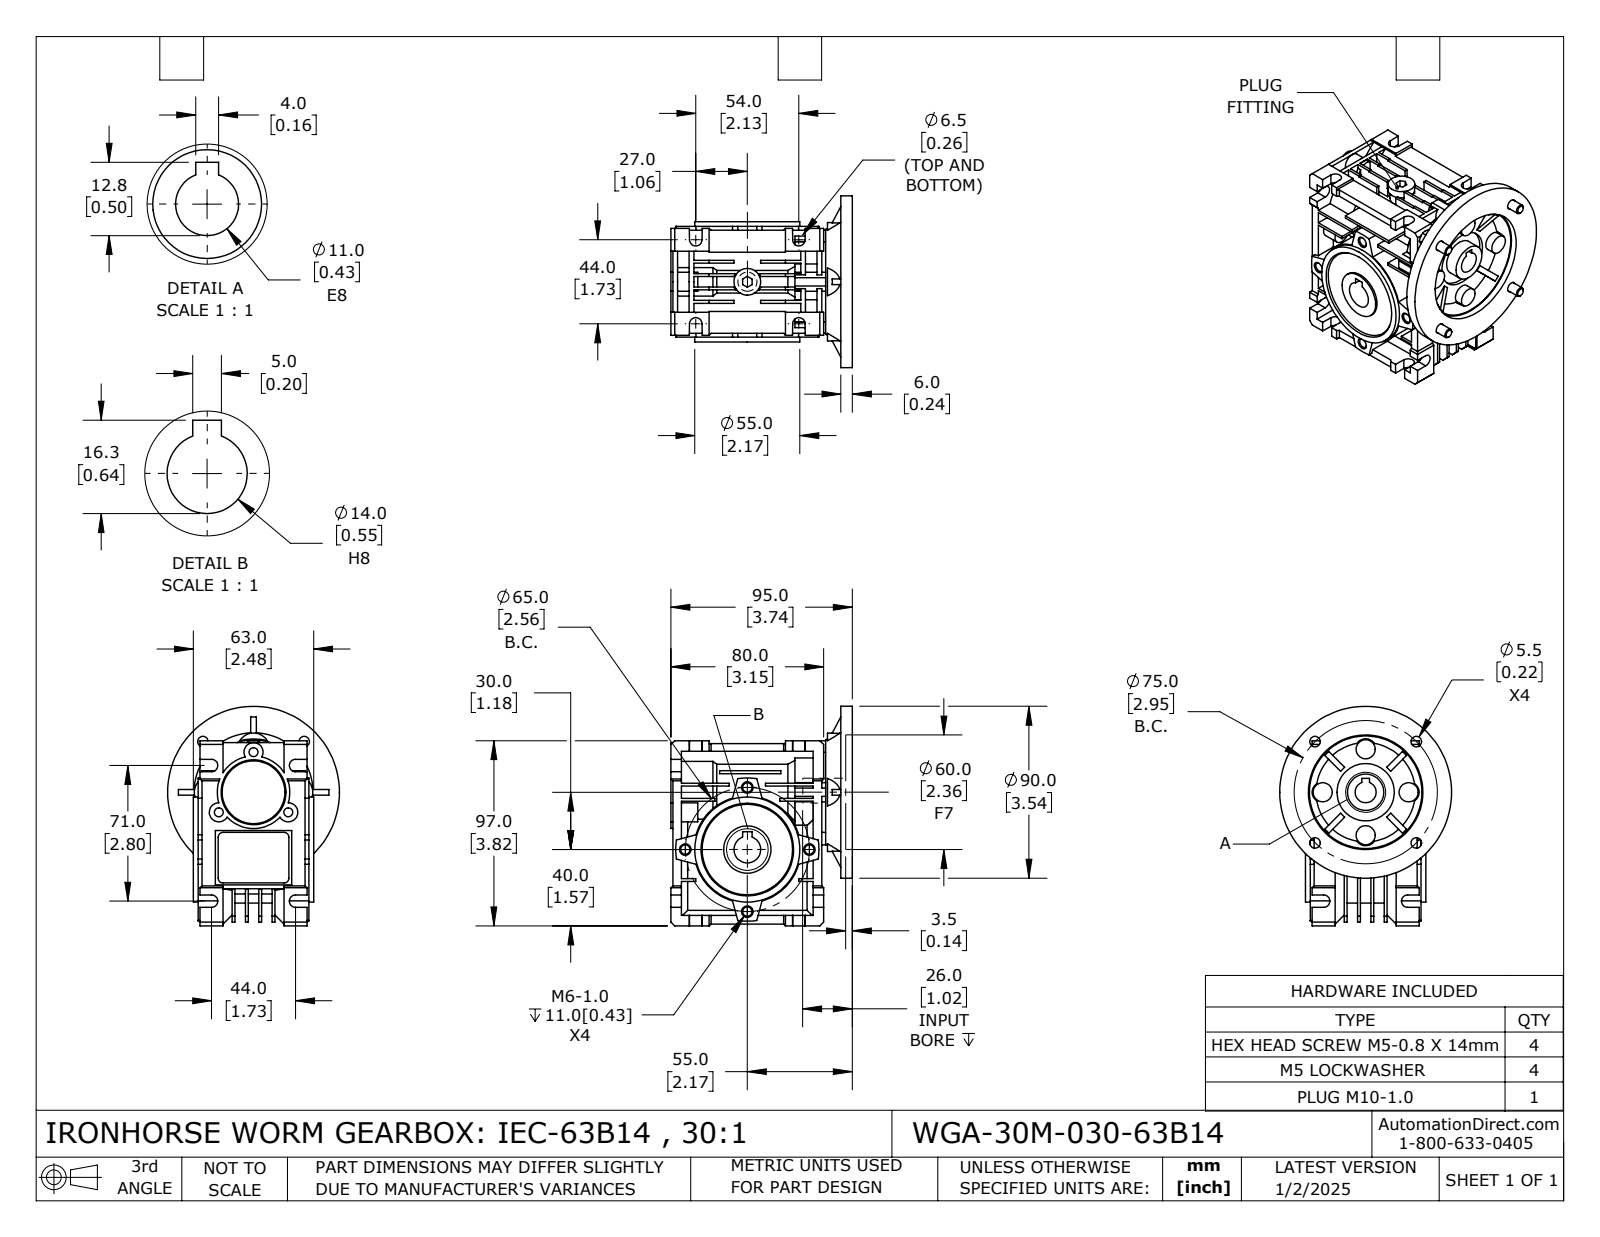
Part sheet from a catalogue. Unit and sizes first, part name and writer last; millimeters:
Units: millimetres
Overall size (bounding box): 115 × 101.7 × 90
Round holes (diameter × count): ⌀4.92 ×4, ⌀5.1 ×4, ⌀5.5 ×4, ⌀4.65 ×3, ⌀4.92 ×2, ⌀9 ×1, ⌀11 ×1, ⌀11.5 ×1, ⌀14 ×1, ⌀14.5 ×1, ⌀19 ×1, ⌀24.8 ×1
Round bosses / shafts (diameter × count): ⌀10 ×4, ⌀9.2 ×4, ⌀5 ×4, ⌀90 ×1, ⌀56 ×1, ⌀55 ×1, ⌀38 ×1, ⌀37 ×1
Partial cylindrical surfaces — rounded edges, fillets, slot ends (radius × count): R3.25 ×8, R2.5 ×4, R5.5 ×4, R8.5 ×4, R5 ×3, R7.5 ×1, R17 ×1, R21.5 ×1
Main face-to-face distances: 1.5, 7, 5.5, 1, 14, 4.5, 8.5, 6, 10, 2
Hole centre spacings: 32.5, 37.5, 45.96, 53.04, 21, 18.06, 27.09, 36.37
Volume: 339 639 mm³ · Surface area: 112 960 mm²
Bodies: 14 solids, 905 faces (566 planar, 239 cylindrical, 100 other)
Part name (STEP PRODUCT): WGA-30M-030-63B14
STEP written by: SolidWorks 2024 (CONFIG_CONTROL_DESIGN)
